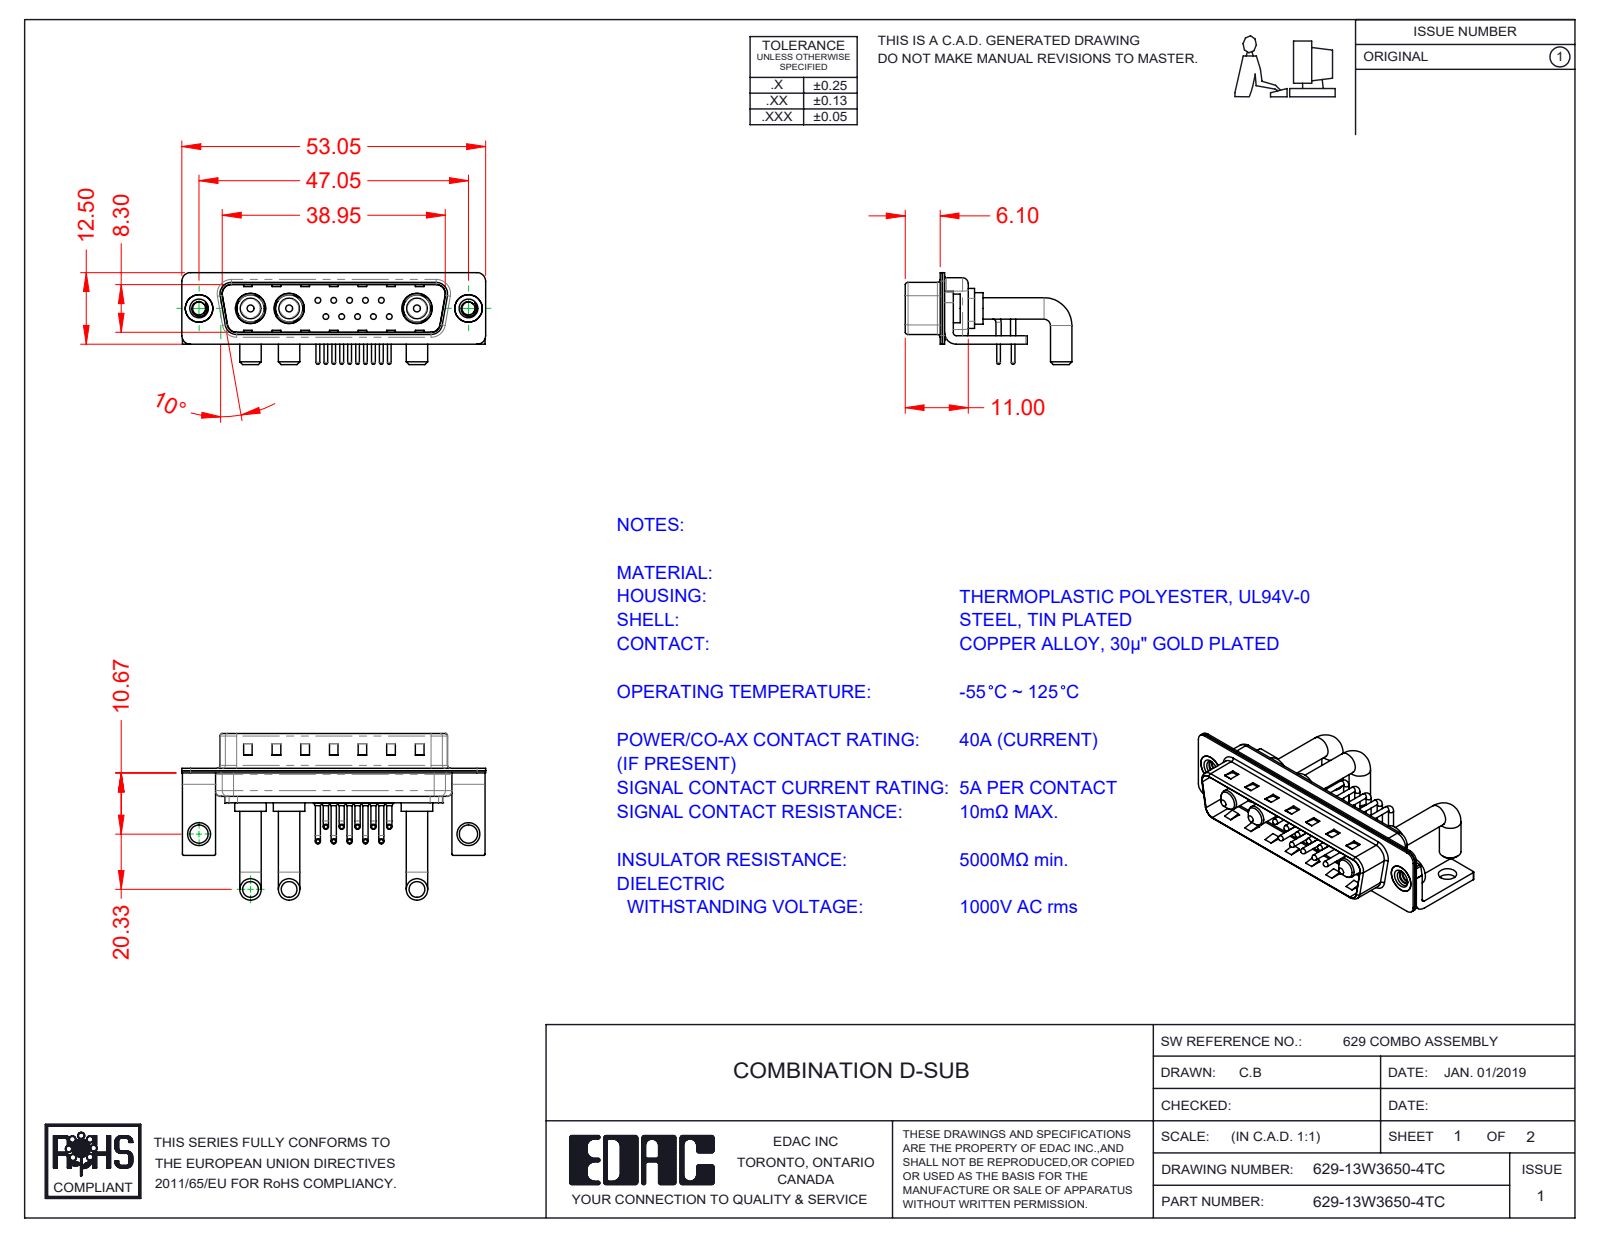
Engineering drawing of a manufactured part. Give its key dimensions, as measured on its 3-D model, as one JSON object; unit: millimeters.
{"part_name": "629Combo Contact Row 1; 629Combo Housing_13W3; Power Pin_Ext 40A RA; 629Combo Contact Row 2 (+5 more)", "step_written_by": "SolidWorks 2020 (CONFIG_CONTROL_DESIGN)", "units": "millimeters", "bodies": {"solids": 23, "faces": 1653, "planar": 861, "cylindrical": 584, "other": 208}, "overall_size": [53.05, 29.11, 16.05], "volume_mm3": 3977, "surface_area_mm2": 8397, "round_holes": [[0.75, 10], [1.6, 10], [2, 10], [4.85, 3], [5.3, 3], [2.26, 2], [3.2, 2], [4, 2], [4.8, 2]], "round_bosses_or_shafts": [[0.9, 20], [1.5, 10], [1, 10], [0.65, 10], [3.75, 6], [5.5, 3], [5.2, 3], [4.75, 3]], "partial_cylinders_radius": [[0.25, 16], [1.5, 16], [2, 13], [1.01, 10], [0.5, 9], [1.6, 8], [0.6, 4], [0.65, 4]], "face_to_face_distances": [0.4, 0.8, 9.5, 9.1, 1.5, 8.7, 9.9, 0.6, 1.2, 5.2], "hole_center_spacings": [3.16, 2.77, 5.04, 5.54, 7.49, 5.03, 8.31, 10.11]}
